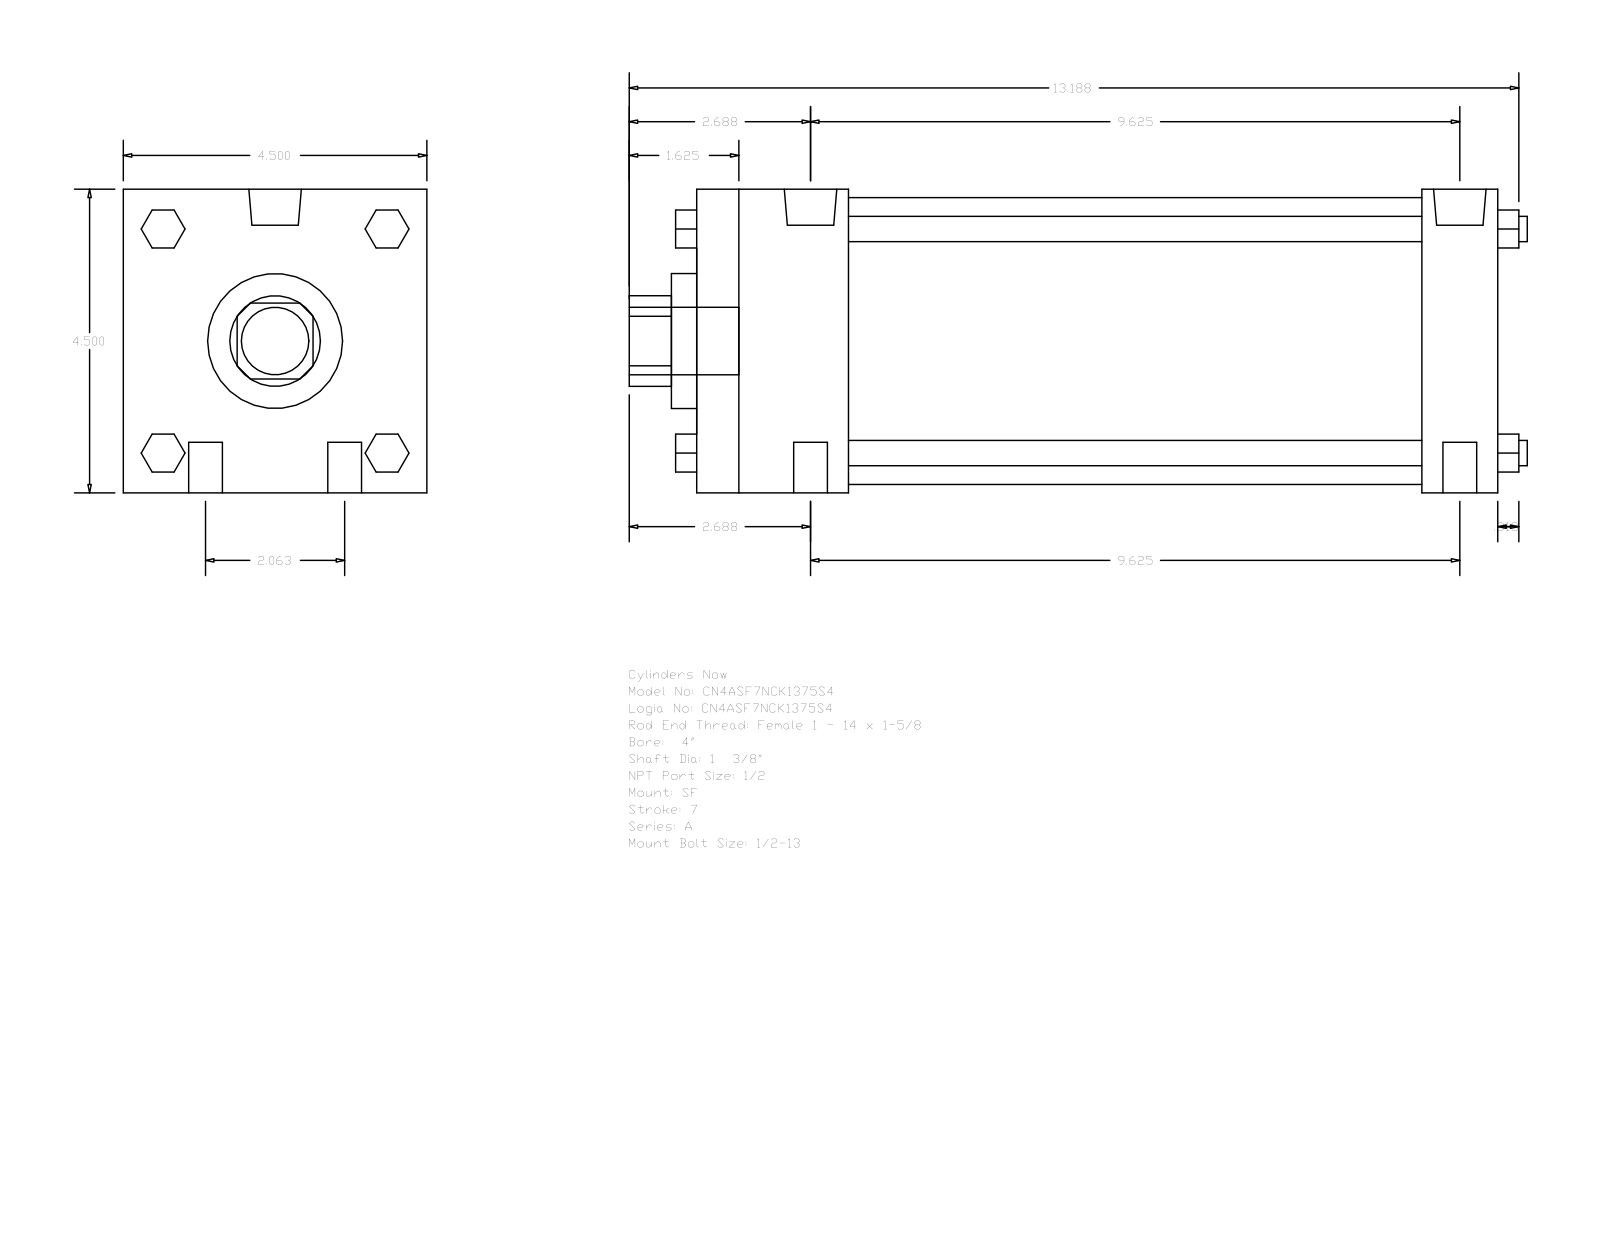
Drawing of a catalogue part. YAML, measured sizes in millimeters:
part_name: "A_SF__0400_1.375"
step_written_by: "GSSL Pune (CONFIG_CONTROL_DESIGN)"
units: millimeters
bodies: {solids: 0, faces: 124, planar: 94, cylindrical: 30, other: 0}
overall_size: [338.14, 114.3, 114.3]
round_holes:
  - {diameter: 34.92, count: 1}
  - {diameter: 50.8, count: 1}
  - {diameter: 107.95, count: 1}
round_bosses_or_shafts:
  - {diameter: 12.7, count: 4}
  - {diameter: 9.53, count: 4}
  - {diameter: 19.77, count: 2}
  - {diameter: 8.73, count: 2}
  - {diameter: 25.4, count: 1}
partial_cylinders:
  - {radius: 17.06, count: 1}
face_to_face_distances: [114.3, 301.62, 28.57, 273.05, 57.15, 215.9, 244.47, 14.29, 9.52, 66.67]
